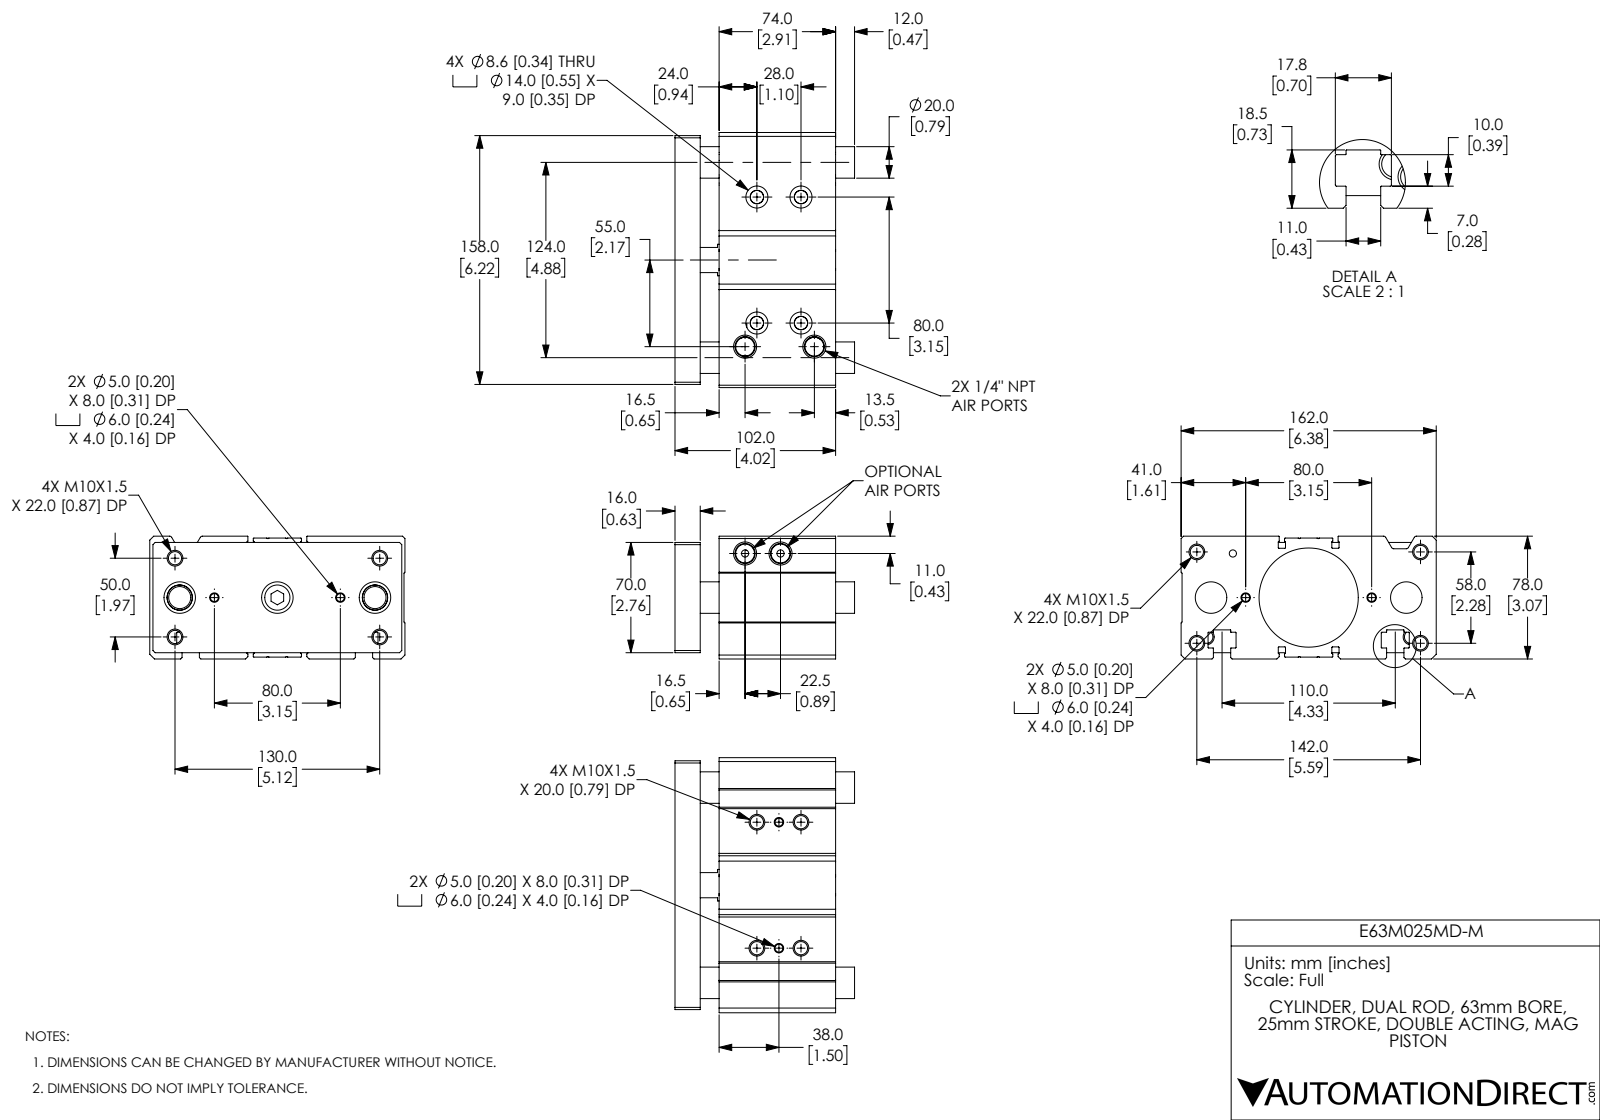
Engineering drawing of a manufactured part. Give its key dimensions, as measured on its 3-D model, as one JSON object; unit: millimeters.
{"part_name": "E63M025MD-M; E63M025MD-M_ENDPLATE; E63M025MD-M_BODY", "step_written_by": "SolidWorks 2019 (CONFIG_CONTROL_DESIGN)", "units": "millimeters", "bodies": {"solids": 5, "faces": 421, "planar": 139, "cylindrical": 190, "other": 92}, "overall_size": [162, 114, 78], "volume_mm3": 947439, "surface_area_mm2": 176756, "round_holes": [[8.38, 12], [5, 4], [6, 4], [8.6, 4], [14, 4], [4.57, 3], [10, 3], [20, 3], [16, 2], [20, 1], [63, 1], [63, 1]], "round_bosses_or_shafts": [[16, 1]], "partial_cylinders_radius": [[0.2, 32], [0.4, 28], [1.5, 4], [0.3, 2]], "face_to_face_distances": [74, 12, 28, 16, 86, 102, 4, 78, 95.25, 79.25], "hole_center_spacings": [7.21, 14, 25.18, 30.36, 35.36, 42.45, 54.33, 69.64]}
